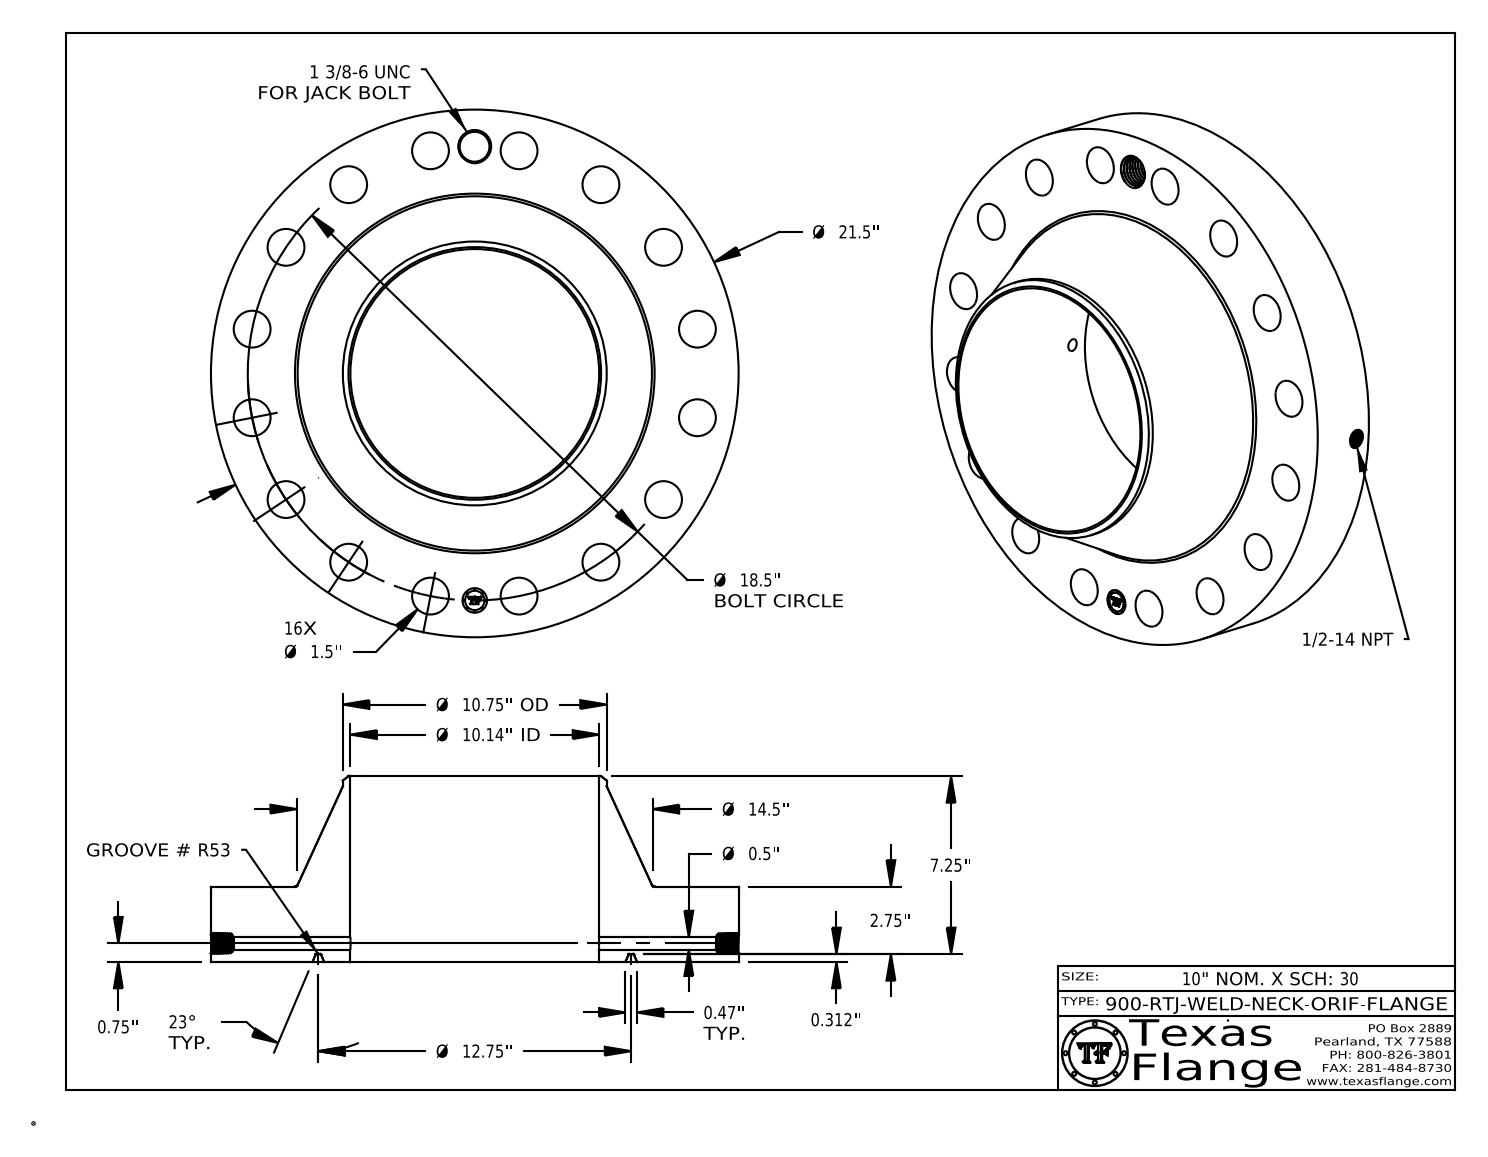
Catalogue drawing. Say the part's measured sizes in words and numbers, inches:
The part is named "900-RTJ-WELD-NECK". Its 3-D file was written by "CATIA V5 STEP AP214 (AUTOMOTIVE_DESIGN)". It is 1 solid with 813 faces: 370 planar, 114 cylindrical and 329 other. Overall it measures 21.5 by 21.5 by 7.562 inches. Its volume is 956.3 cubic inches and its surface area 1 352 square inches. Round holes: 16 of diameter 1.5, 1 of diameter 0.5, 1 of diameter 0.672, 1 of diameter 1, 1 of diameter 1.219, 1 of diameter 10.136. Round bosses or shafts: 8 of diameter 0.061, 1 of diameter 21.5, 1 of diameter 10.75, 1 of diameter 0.788. The main face-to-face distances are 3.062, 0.312, 2.75, 7.562, 7.25, 4.5, 3.047, 2.735, 0.015, 4.515. The hole center spacings are 10.278, 17.092, 3.609, 9.25, 7.08, 7.08, 9.25, 13.081.
